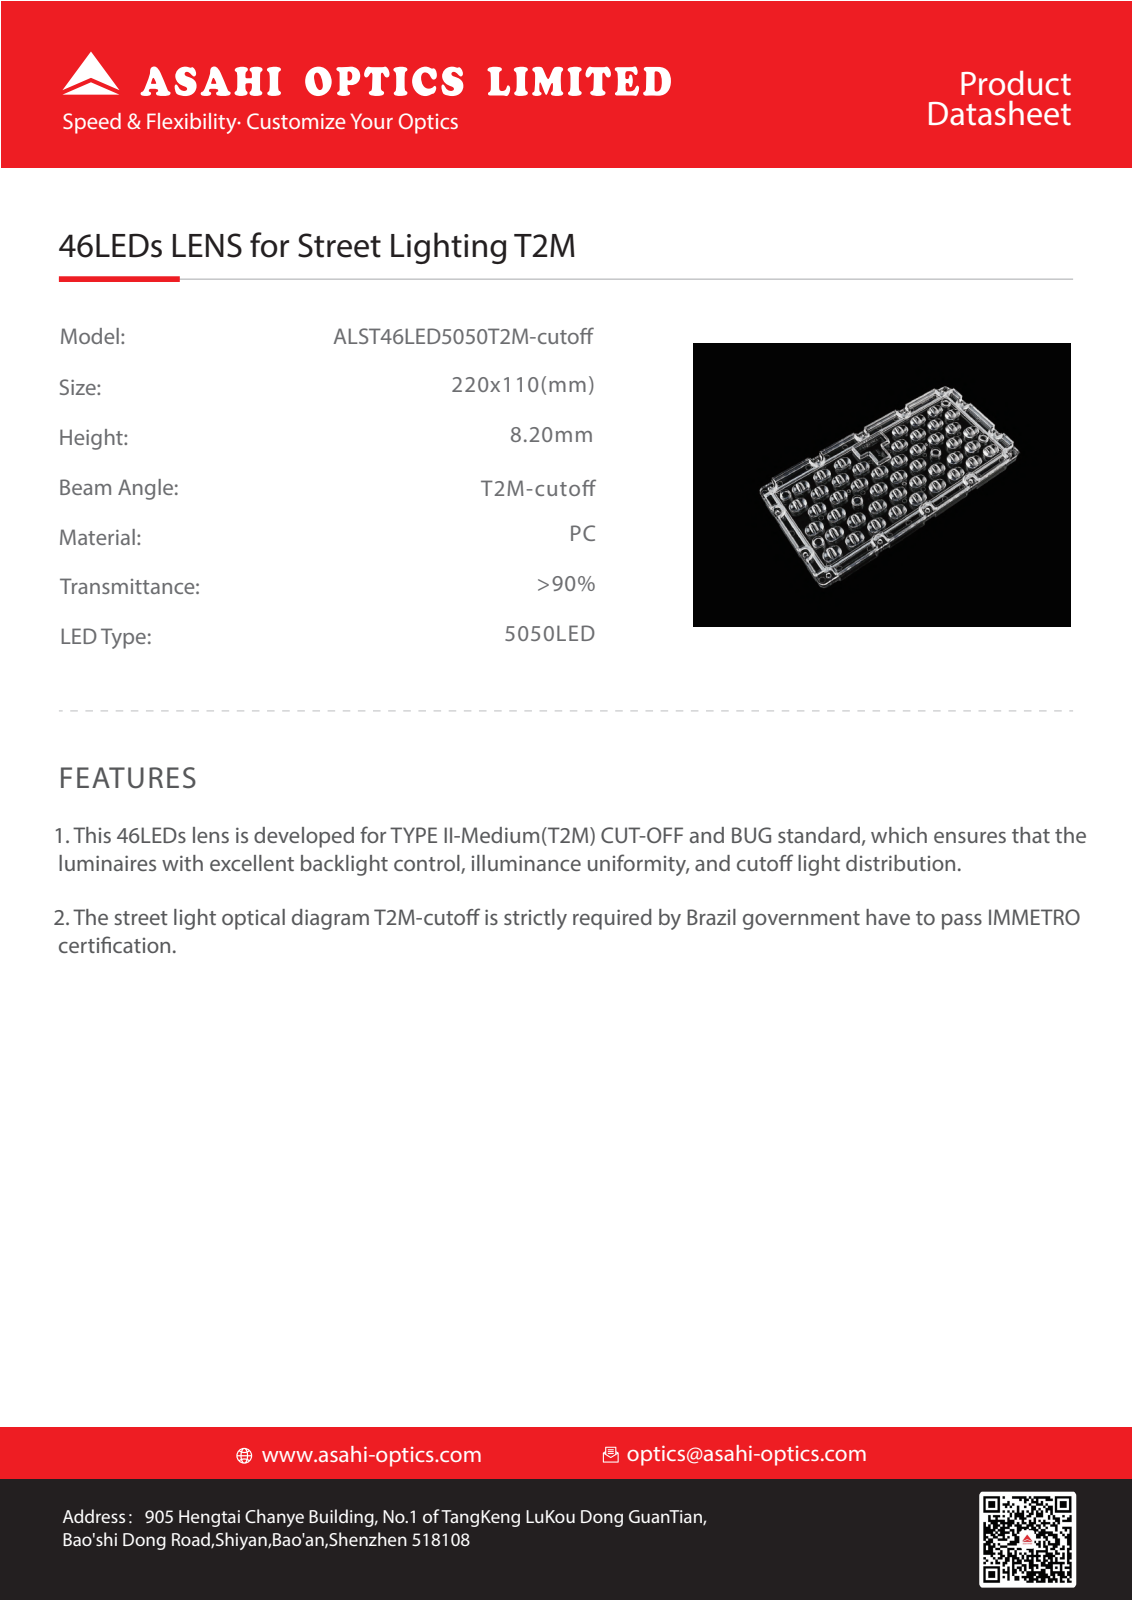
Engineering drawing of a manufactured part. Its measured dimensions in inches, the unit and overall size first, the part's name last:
Units: inches
Overall size (bounding box): 8.657 × 4.327 × 0.323
Partial cylindrical surfaces — rounded edges, fillets, slot ends (radius × count): R0.039 ×77, R0.059 ×32, R0.02 ×20, R0.079 ×10, R0.031 ×7, R0.118 ×4, R0.197 ×4
Main face-to-face distances: 0.087, 0.059, 0.146, 0.085, 0.026, 0.061, 0.185, 0.244, 0.159, 0.098
Volume: 4.705 in³ · Surface area: 99.25 in²
Bodies: 1 solid, 1717 faces (513 planar, 207 cylindrical, 997 other)
Part name (STEP PRODUCT): M46
STEP written by: PRO/ENGINEER BY PARAMETRIC TECHNOLOGY CORPORATION, 2015070 (CONFIG_CONTROL_DESIGN)
